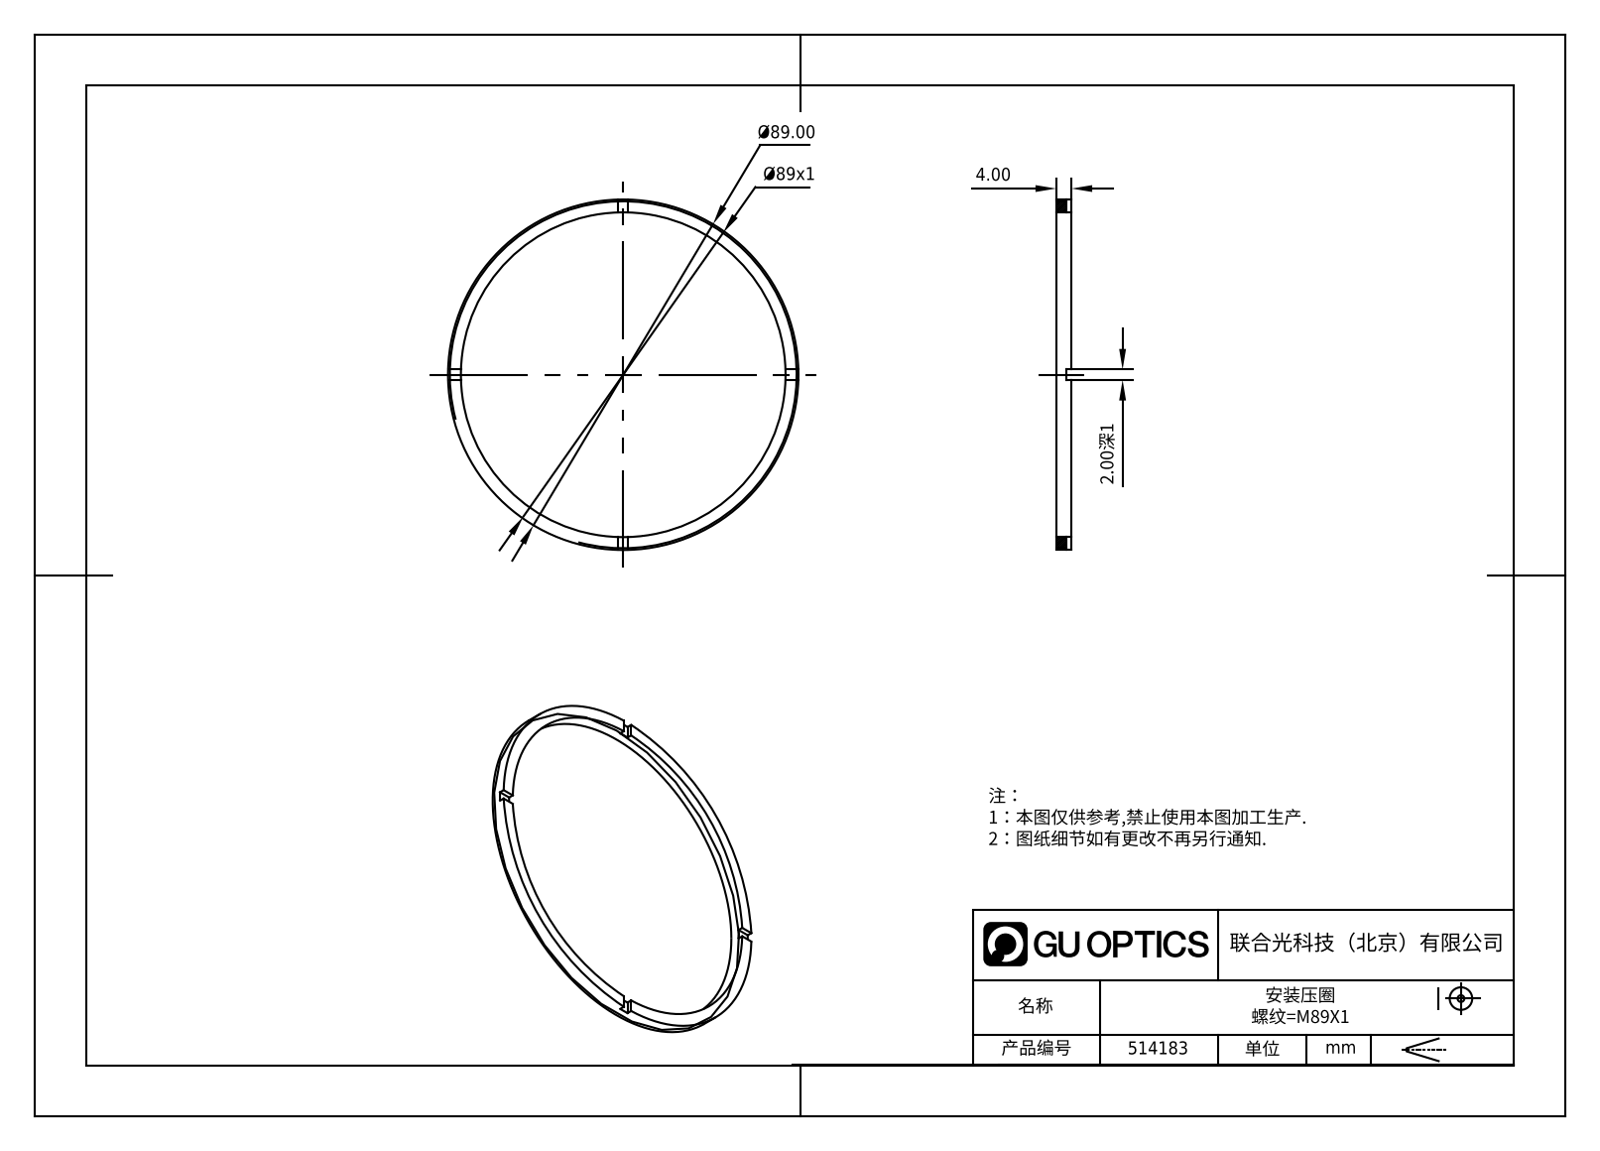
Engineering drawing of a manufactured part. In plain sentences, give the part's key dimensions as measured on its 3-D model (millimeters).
The part is named "514183". Its 3-D file was written by "SolidWorks 2020 (CONFIG_CONTROL_DESIGN)". It is 1 solid with 21 faces: 17 planar, 4 cylindrical and 0 other. Overall it measures 89 by 89 by 4 millimeters. Its volume is 3 218 cubic millimeters and its surface area 3 790 square millimeters. Round holes: 1 of diameter 83. Round bosses or shafts: 1 of diameter 89. The main face-to-face distances are 4, 3, 1, 2.
